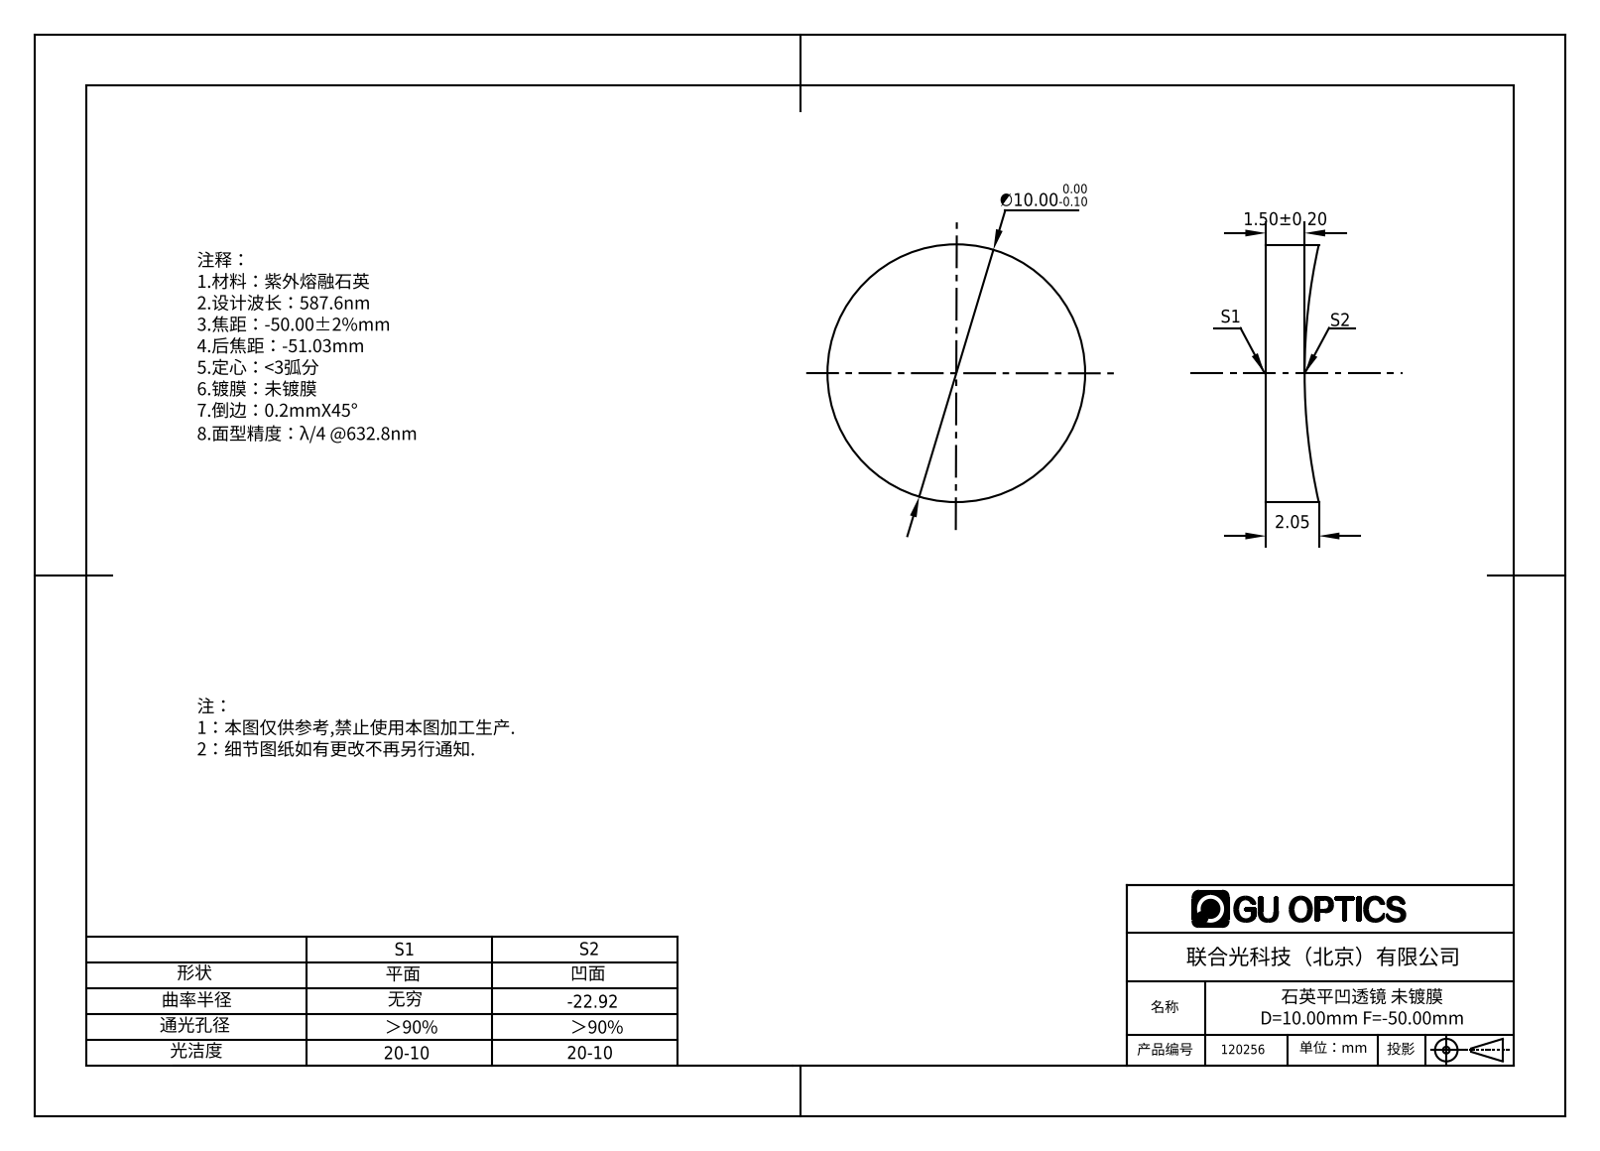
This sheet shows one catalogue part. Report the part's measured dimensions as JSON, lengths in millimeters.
{"part_name": "120256", "step_written_by": "SolidWorks 2016 (AUTOMOTIVE_DESIGN)", "units": "millimeters", "bodies": {"solids": 1, "faces": 5, "planar": 1, "cylindrical": 2, "other": 2}, "overall_size": [10, 10, 2.05], "volume_mm3": 139, "surface_area_mm2": 222, "round_bosses_or_shafts": [[10, 1]]}
